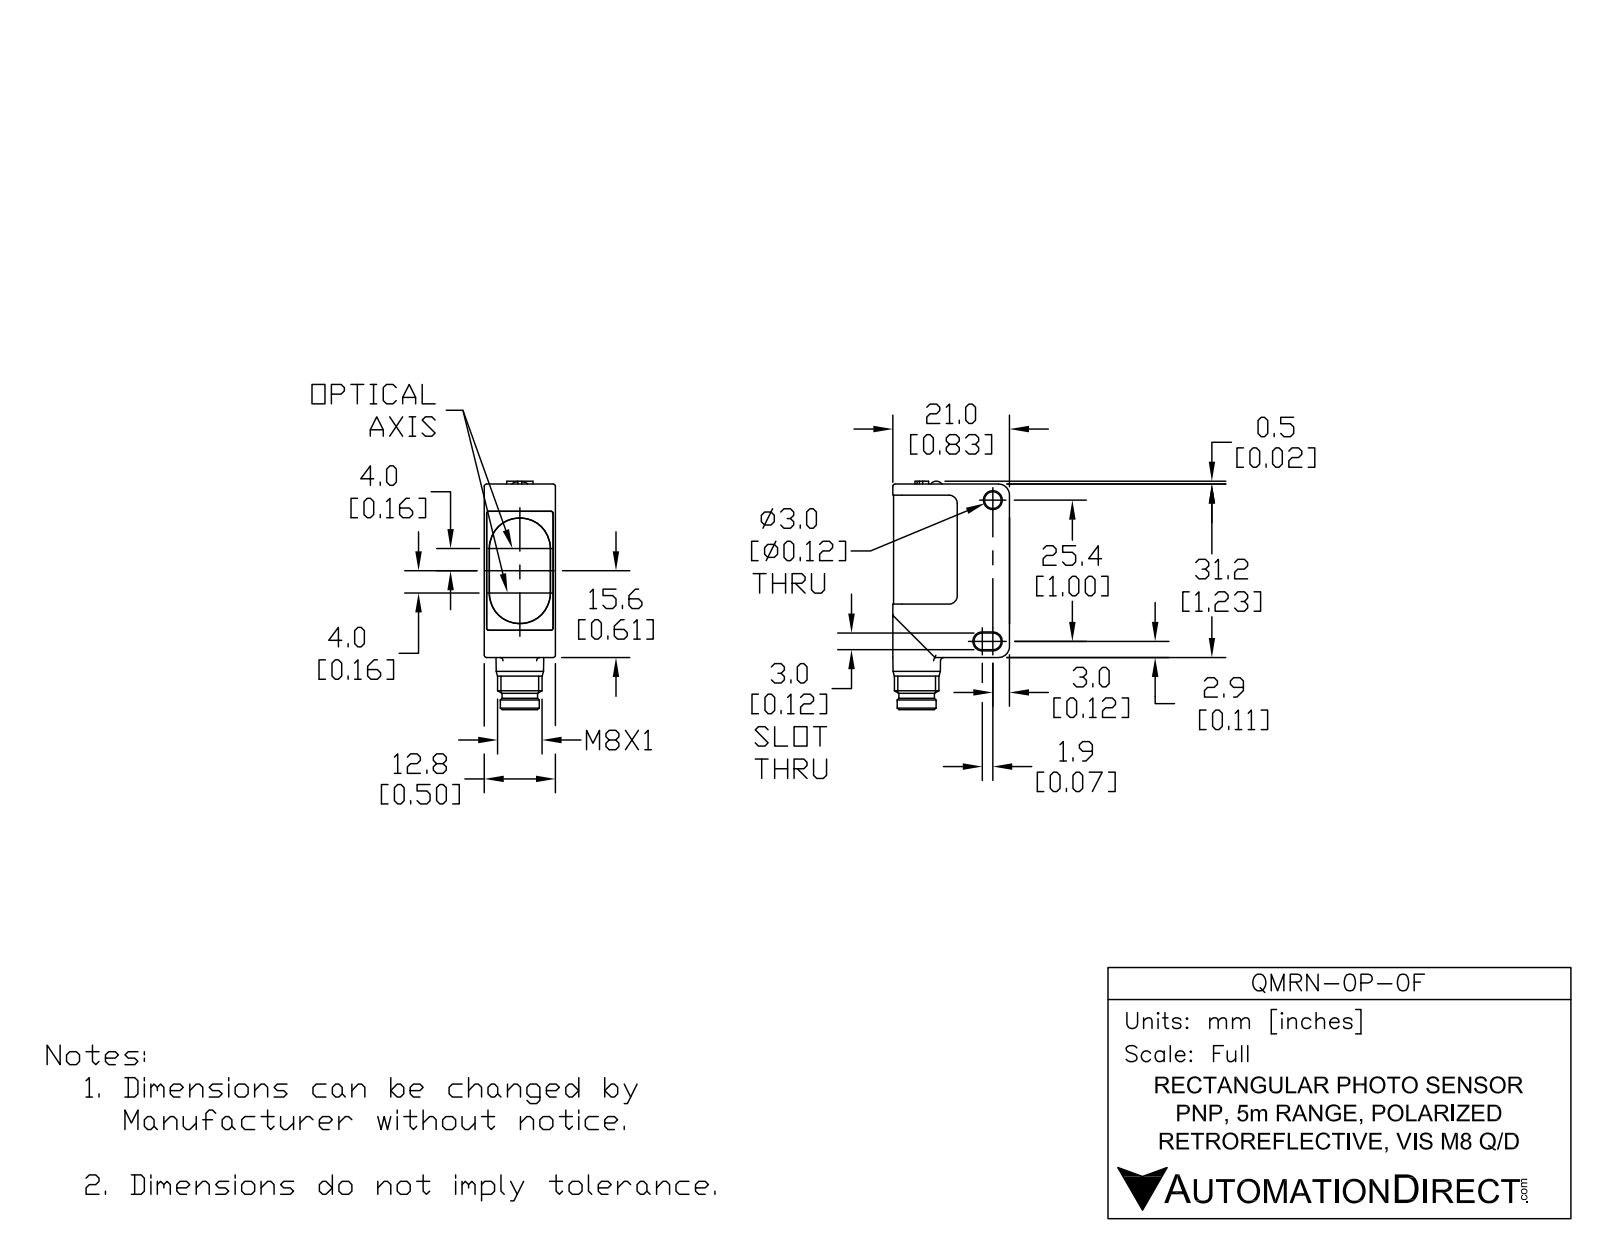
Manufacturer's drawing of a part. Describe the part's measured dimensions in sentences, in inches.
The part is named "QMRN-0P-0F". Its 3-D file was written by "SolidWorks 2017 (AUTOMOTIVE_DESIGN)". It is 7 solids with 272 faces: 125 planar, 100 cylindrical and 47 other. Overall it measures 1.619 by 0.827 by 0.504 inches. Its volume is 0.474 cubic inches and its surface area 7.749 square inches. Round holes: 3 of diameter 0.118, 1 of diameter 0.228. Round bosses or shafts: 4 of diameter 0.039, 2 of diameter 0.138, 1 of diameter 0.315, 1 of diameter 0.276, 1 of diameter 0.252. Partial cylindrical surfaces (rounded edges, fillets, slot ends): 10 of radius 0.016, 9 of radius 0.02, 6 of radius 0.059, 4 of radius 0.024, 4 of radius 0.039, 2 of radius 0.006, 2 of radius 0.044, 2 of radius 0.065. The main face-to-face distances are 0.498, 0.02, 0.504, 0.11, 0.016, 0.492, 0.488, 0.482, 0.059, 0.711. The hole center spacings are 0.04, 0.205, 0.245.
